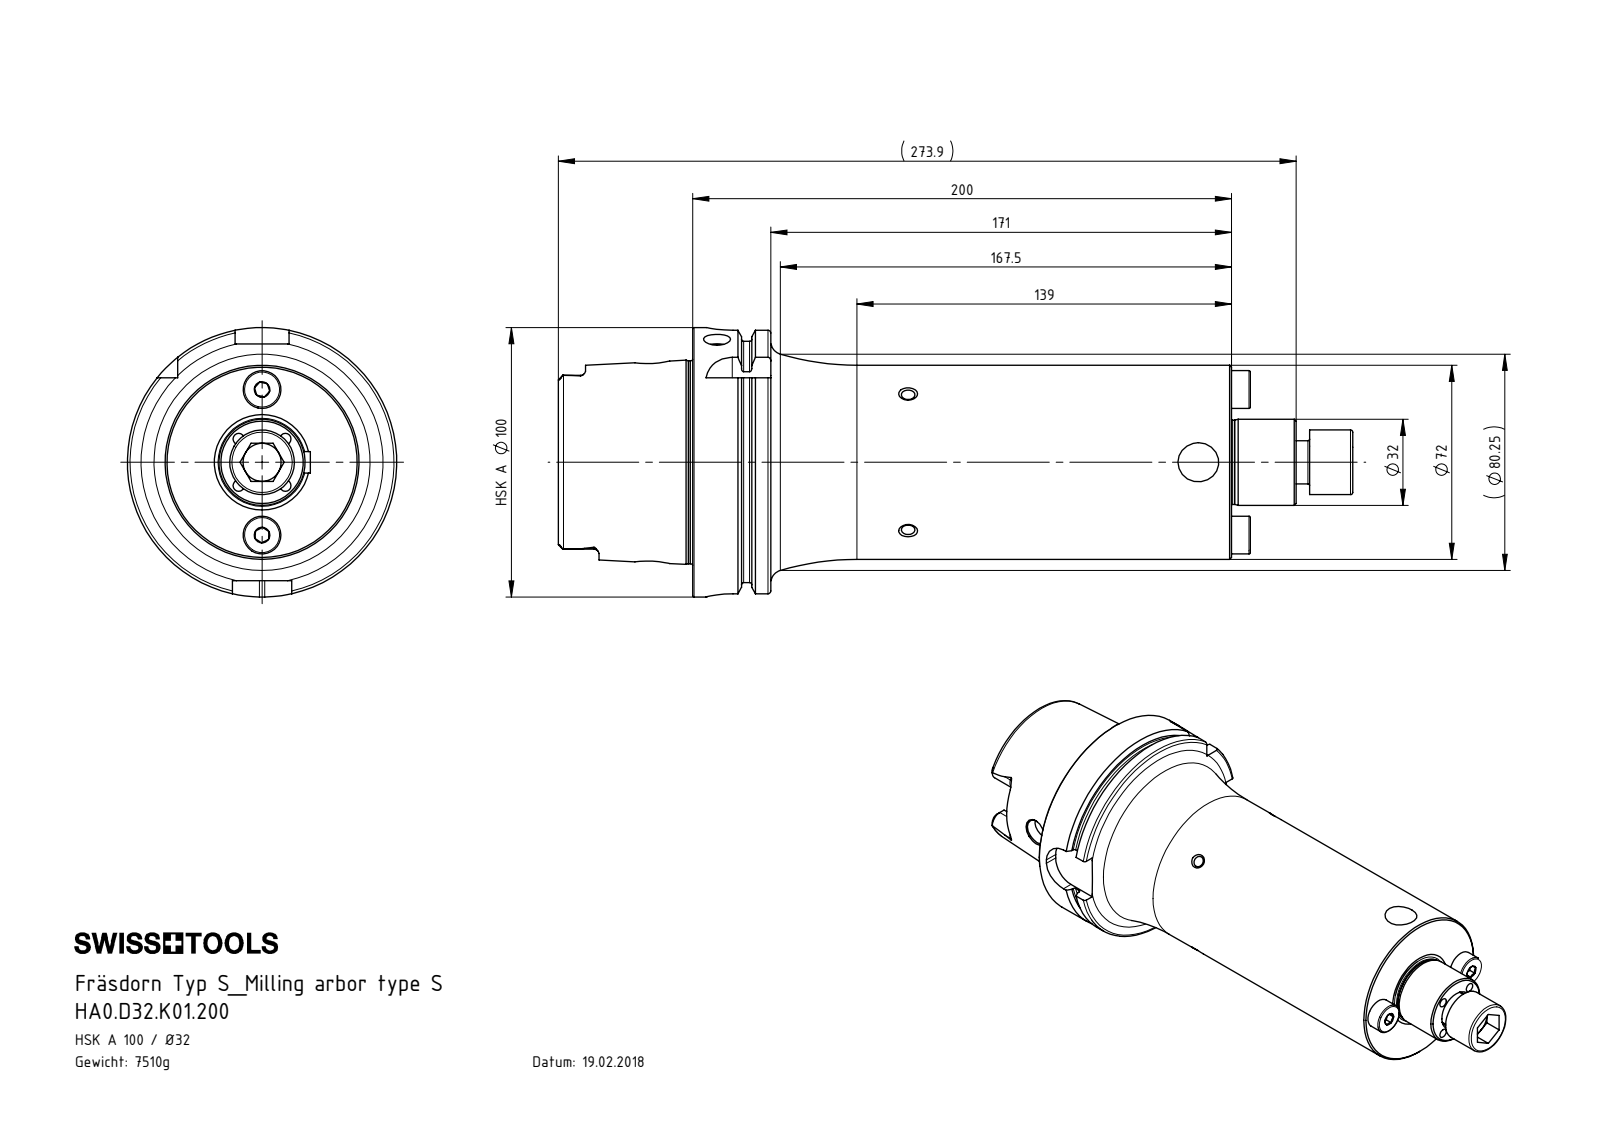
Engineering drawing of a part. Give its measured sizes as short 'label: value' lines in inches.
name: HA0-D32.K01.200_C_Fertigbearbeitung; D32-ER2.001.022_B; HA0.D32.K01.200; DIN 6885 - 8x7x16 (+1 more)
written by: SolidWorks 2017 (AUTOMOTIVE_DESIGN)
unit: in
bodies: 5 solids, 373 faces (91 planar, 119 cylindrical, 163 other)
size: 11.61 × 3.937 × 3.937
volume: 59.06 in³; area: 168.1 in²
holes: 6× ⌀0.165, 6× ⌀0.197, 4× ⌀0.472, 3× ⌀0.394, 1× ⌀0.551, 1× ⌀0.669, 1× ⌀0.886, 1× ⌀1.024, 1× ⌀2.087, 1× ⌀2.48
bosses: 2× ⌀0.551, 2× ⌀0.236, 2× ⌀0.181, 1× ⌀3.937, 1× ⌀3.62, 1× ⌀2.963, 1× ⌀2.835, 1× ⌀1.26
rounds: 6× R0.075, 4× R0.157, 4× R0.192, 4× R0.394
face distances: 7.874, 0.49, 7.384, 1.14, 0.65, 6.734, 1.965, 2.455, 3.104, 9.839
hole spacings: 0.482, 0.682, 0.798, 1.445, 4.333, 0.964, 1.063, 2.126
